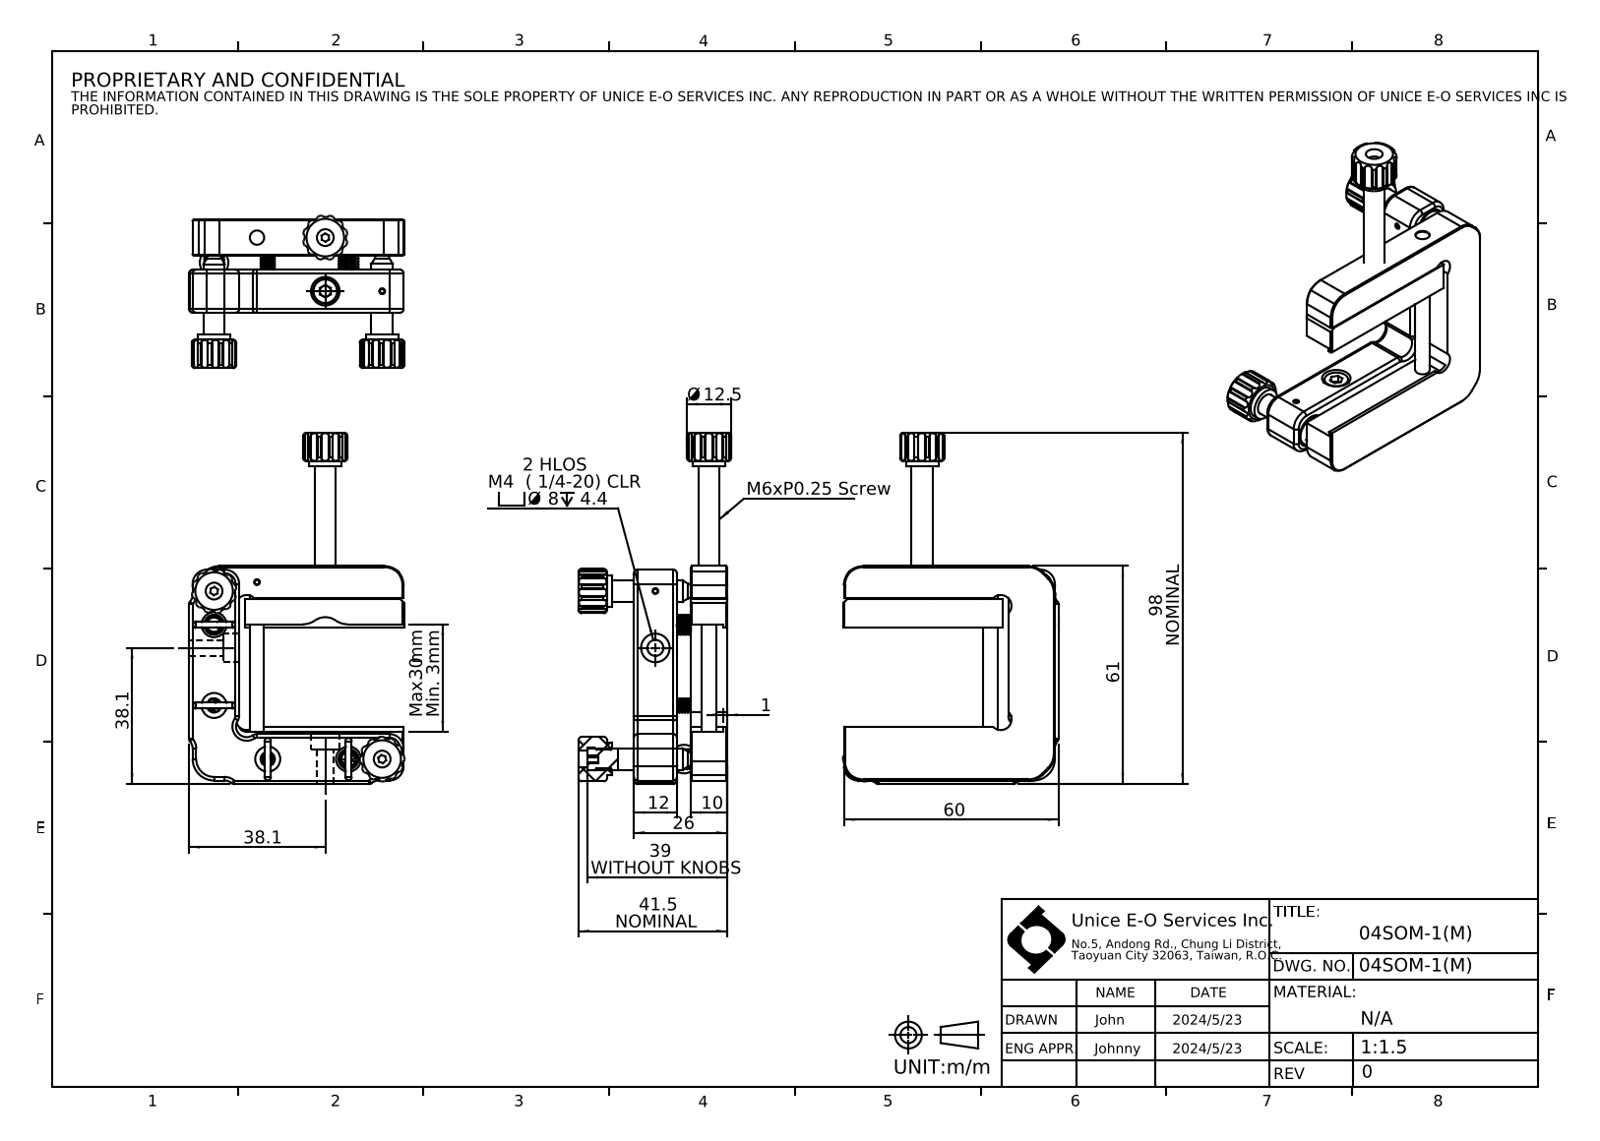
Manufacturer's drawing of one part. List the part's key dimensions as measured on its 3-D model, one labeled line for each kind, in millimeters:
Part name (STEP PRODUCT): 04SOM-1M
STEP written by: SolidWorks 2022 (CONFIG_CONTROL_DESIGN)
Units: millimetres
Bodies: 0 solids, 474 faces (142 planar, 254 cylindrical, 78 other)
Overall size (bounding box): 98.3 × 60.25 × 42.7
Round holes (diameter × count): ⌀1.1 ×4, ⌀1.8 ×4, ⌀7 ×4, ⌀1.6 ×3, ⌀4.7 ×3, ⌀5 ×2, ⌀8 ×2, ⌀9.5 ×2, ⌀4 ×1, ⌀6 ×1, ⌀6.5 ×1
Round bosses / shafts (diameter × count): ⌀1.5 ×10, ⌀9 ×3, ⌀6 ×2
Partial cylindrical surfaces — rounded edges, fillets, slot ends (radius × count): R0.3 ×70, R1.5 ×37, R1 ×20, R6 ×11, R0.9 ×8, R3 ×7, R0.75 ×4, R4 ×4
Main face-to-face distances: 10, 14, 16, 1, 13, 4, 26, 12, 60, 9
Hole centre spacings: 22.6, 9.4, 15.9, 16.35, 17.7, 22, 32, 35.34
